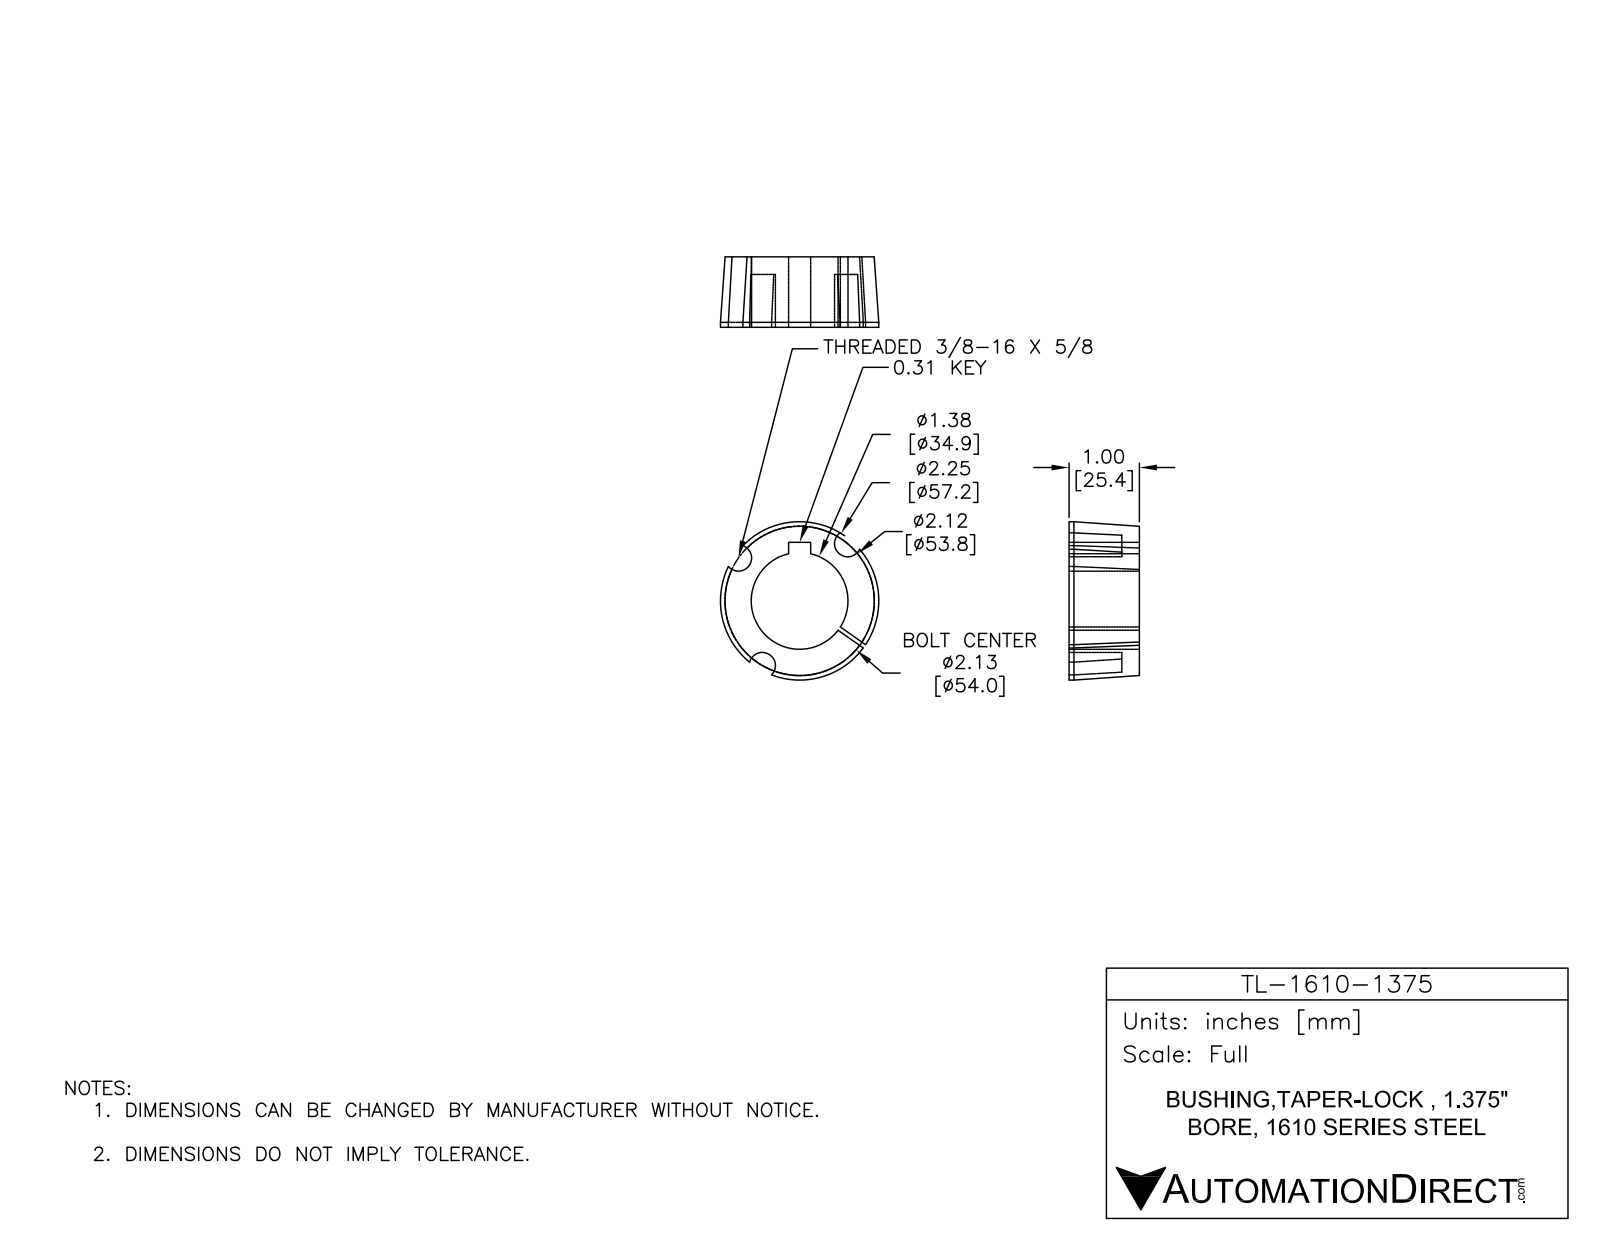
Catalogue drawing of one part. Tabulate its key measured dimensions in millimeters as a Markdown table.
| quantity | value |
| --- | --- |
| part name | TL-1610-1375 |
| STEP written by | SolidWorks 2014 (AUTOMOTIVE_DESIGN) |
| units | millimeters |
| bodies | 1 solid, 25 faces (9 planar, 13 cylindrical, 3 other) |
| overall size | 57.2 × 57.2 × 25.4 |
| volume | 33 680 mm³ |
| surface area | 11 010 mm² |
| round holes (diameter × count) | 34.9 × 1 |
| round bosses / shafts (diameter × count) | 57.2 × 1 |
| partial cylindrical surfaces (radius × count) | 4.8 × 3 |
| main face-to-face distances | 25.4, 1.4, 8, 6.4, 19.1 |
